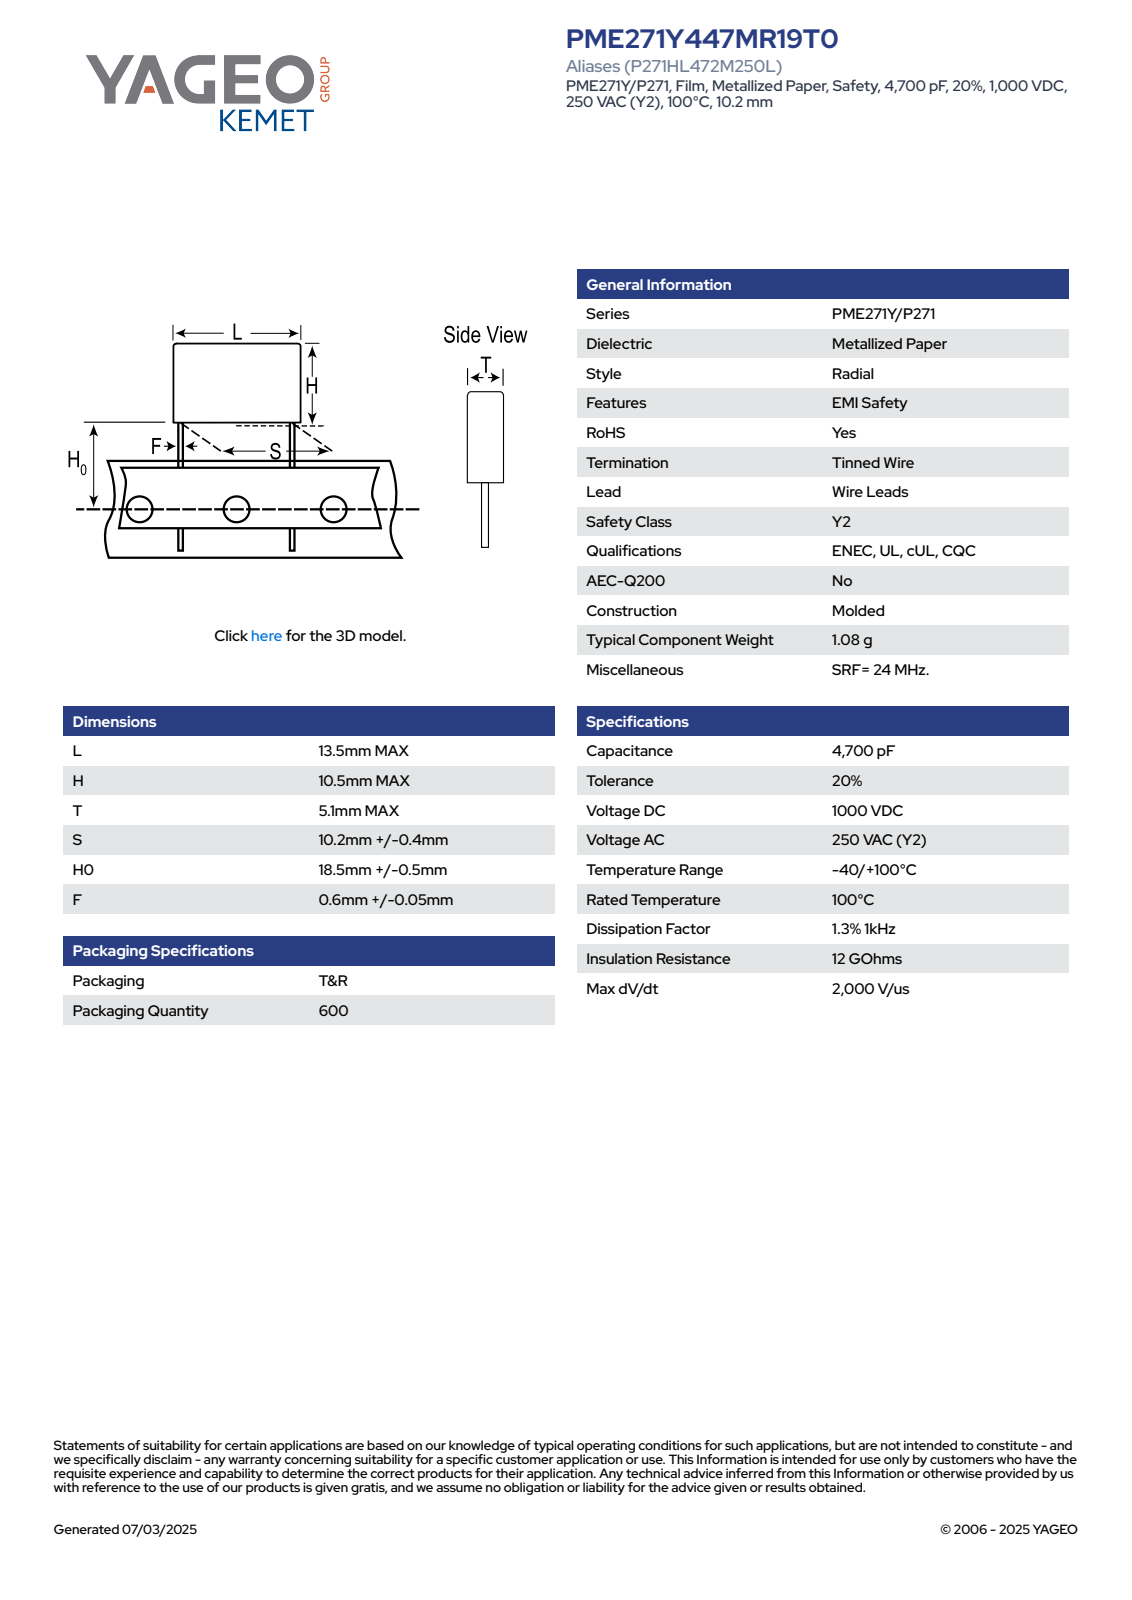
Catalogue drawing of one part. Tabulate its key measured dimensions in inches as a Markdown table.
| quantity | value |
| --- | --- |
| part name | CFR_MOLDED_13.5X10.5X5.1_L13.5H10.5T5.1S10.2H019F0.65 |
| STEP written by | SolidWorks 2014 (AUTOMOTIVE_DESIGN) |
| units | inches |
| bodies | 4 solids, 73 faces (65 planar, 8 cylindrical, 0 other) |
| overall size | 1.161 × 0.531 × 0.201 |
| volume | 0.045 in³ |
| surface area | 0.941 in² |
| round bosses / shafts (diameter × count) | 0.026 × 2 |
| partial cylindrical surfaces (radius × count) | 0.02 × 4 |
| main face-to-face distances | 0.201, 0.413, 0.531, 0.748, 1.161, 0.048, 0.969, 0.221, 0.193, 0.921 |
